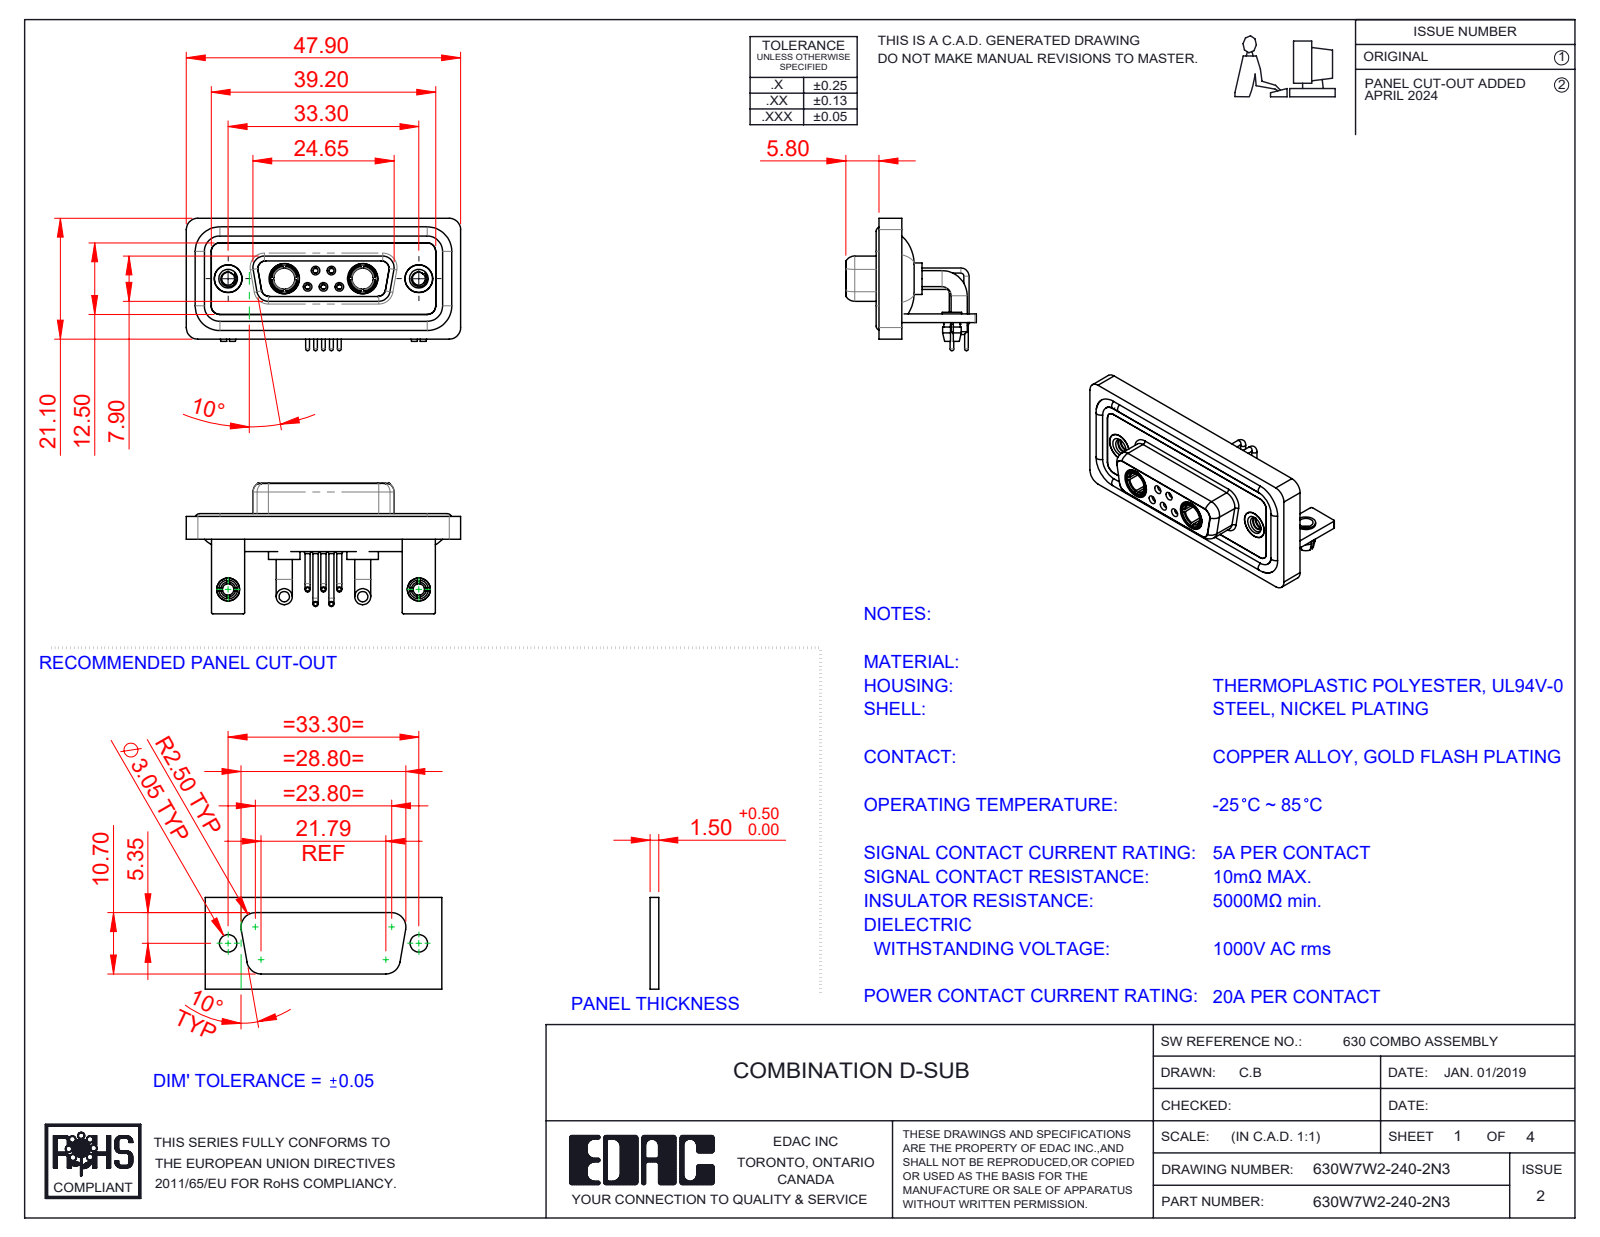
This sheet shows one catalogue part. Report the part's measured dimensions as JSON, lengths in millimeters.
{"part_name": "630Combo Contact Row 2_50 Contacts; 630Combo Contact Row 1_50 Contacts; 630Combo Stabilizer Bracket_50 Contacts; 630Combo Housing_7W2 (+7 more)", "step_written_by": "SolidWorks 2023 (CONFIG_CONTROL_DESIGN)", "units": "millimeters", "bodies": {"solids": 20, "faces": 947, "planar": 306, "cylindrical": 409, "other": 232}, "overall_size": [47.9, 23.12, 22.8], "volume_mm3": 6599, "surface_area_mm2": 11151, "round_holes": [[2, 7], [0.9, 5], [1.1, 5], [1.5, 5], [4.85, 4], [1.6, 3], [1.7, 2], [2.26, 2], [2.5, 2], [3.2, 2], [3.7, 2], [4, 2]], "round_bosses_or_shafts": [[1.6, 6], [0.9, 5], [0.65, 5], [2.8, 4], [5.5, 2], [5.2, 2], [4.96, 2], [4.95, 2]], "partial_cylinders_radius": [[2, 21], [1.5, 18], [0.25, 16], [1.35, 12], [1.6, 8], [0.5, 5], [0.6, 4], [0.65, 4]], "face_to_face_distances": [0.4, 2.9, 1.5, 1.8, 3.7, 1.1, 4.1, 1.6, 2.5, 1.4], "hole_center_spacings": [3.16, 2.77, 9.8, 23.5, 33.3, 4.31, 4.33, 5.03]}
